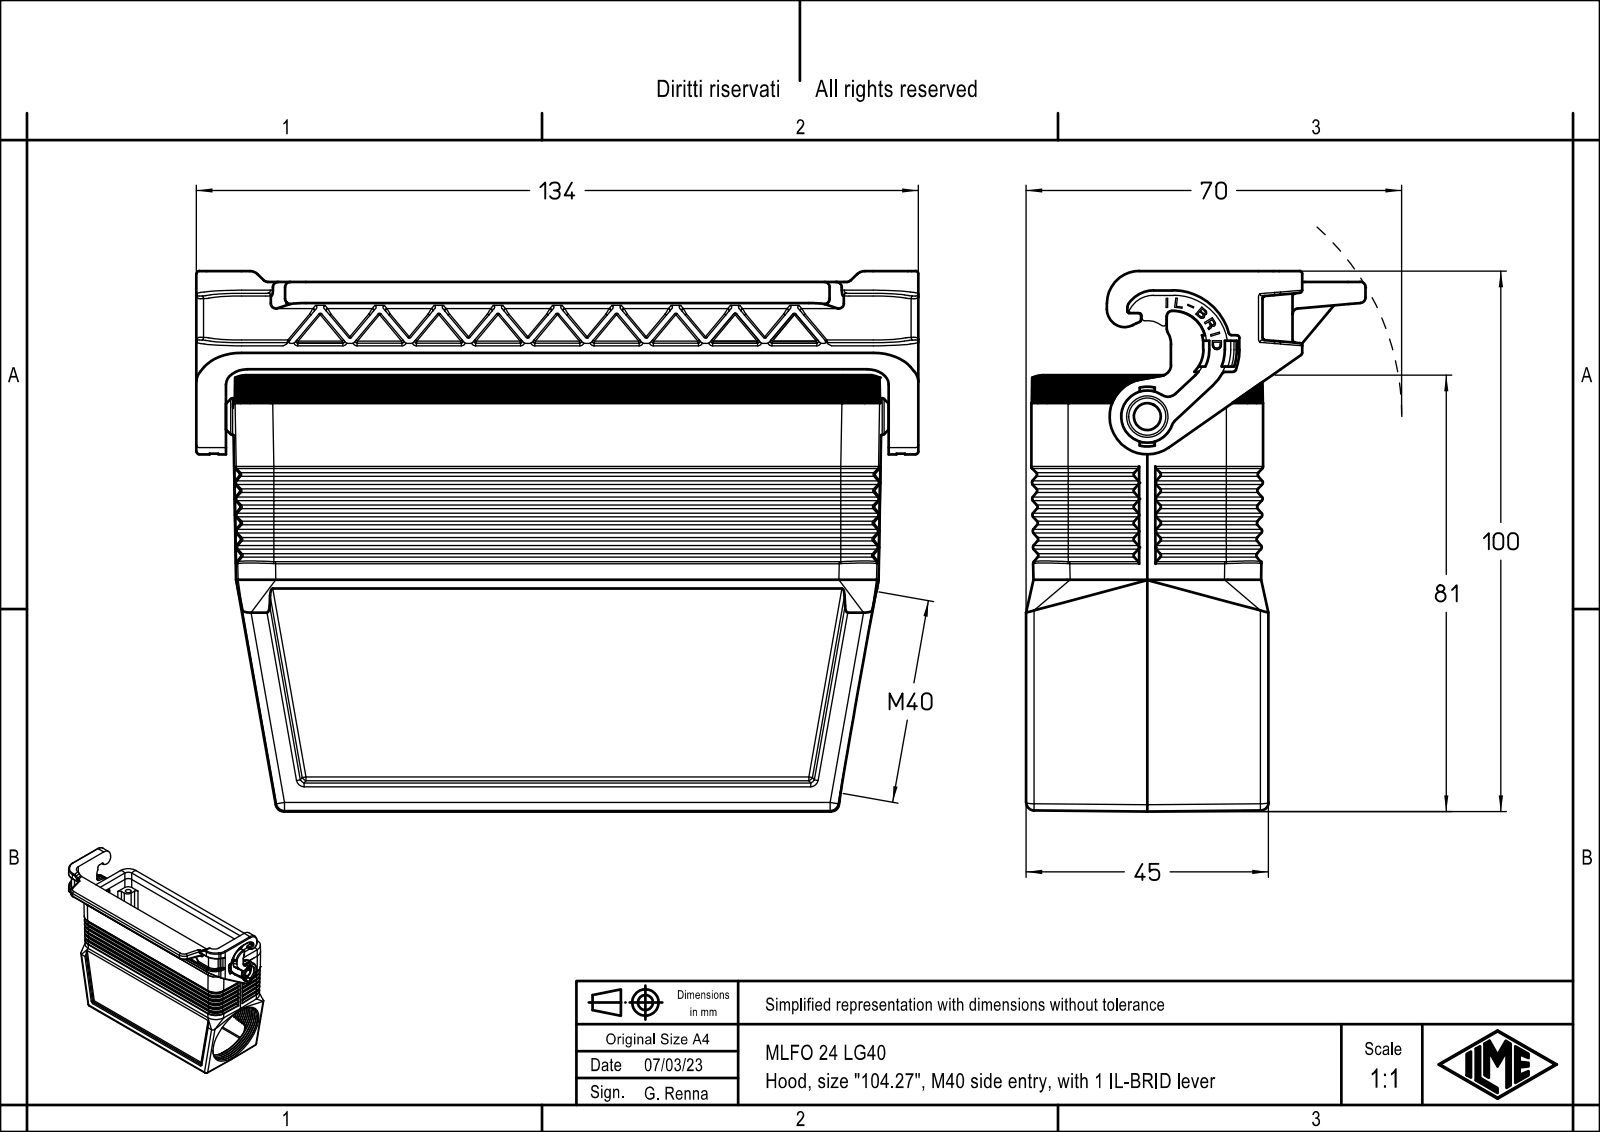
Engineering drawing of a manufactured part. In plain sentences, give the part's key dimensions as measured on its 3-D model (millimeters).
The part is named "MLFO 24 LG40". Its 3-D file was written by "Creo Elements/Direct Modeling 20.1B 02-Apr-2019 (C) Parametric Technology GmbH (AUTOMOTIVE_DESIGN)". It is 1 solid with 1429 faces: 802 planar, 366 cylindrical and 261 other. Overall it measures 134 by 100.25 by 63 millimeters. Its volume is 126 207 cubic millimeters and its surface area 71 601 square millimeters. Round holes: 4 of diameter 3, 4 of diameter 3.5, 1 of diameter 3.25, 1 of diameter 5.4, 1 of diameter 7.7. Round bosses or shafts: 1 of diameter 6.9, 1 of diameter 6.8, 1 of diameter 5.2, 1 of diameter 3.2. Partial cylindrical surfaces (rounded edges, fillets, slot ends): 80 of radius 0.5, 27 of radius 0.1, 23 of radius 1.5, 16 of radius 1, 15 of radius 0.2, 14 of radius 7, 13 of radius 0.33, 12 of radius 3. The main face-to-face distances are 3.75, 39.25, 35.5, 43, 2, 7, 46.25, 3.25, 42.5, 1. The hole center spacings are 27, 104, 107.45.
